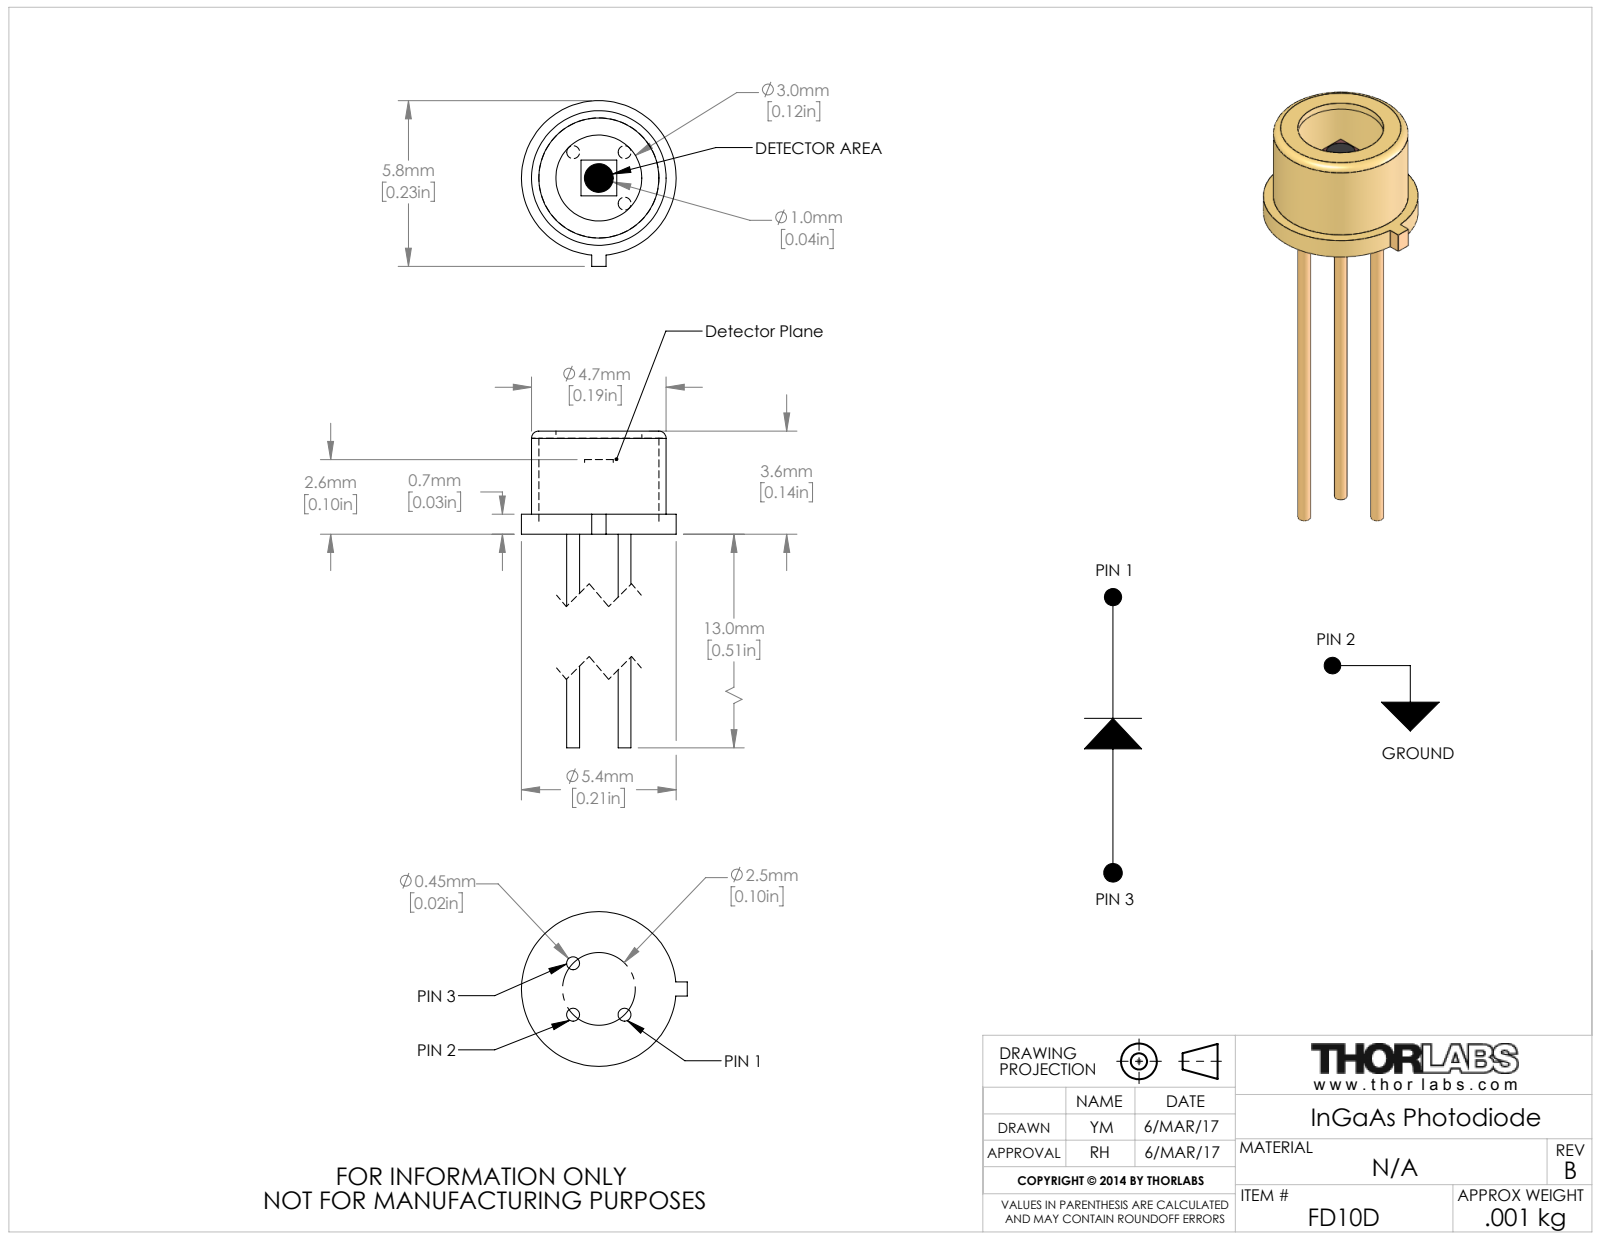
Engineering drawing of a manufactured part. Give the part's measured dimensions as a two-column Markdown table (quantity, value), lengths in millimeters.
| quantity | value |
| --- | --- |
| part name | TTN035386-E0W |
| STEP written by | SolidWorks 2014 (AUTOMOTIVE_DESIGN) |
| units | millimeters |
| bodies | 2 solids, 37 faces (18 planar, 17 cylindrical, 2 other) |
| overall size | 16.6 × 5.79 × 5.4 |
| volume | 31 mm³ |
| surface area | 213 mm² |
| round holes (diameter × count) | 3 × 1, 4.19 × 1 |
| round bosses / shafts (diameter × count) | 0.45 × 3, 5.4 × 1, 4.7 × 1, 1 × 1 |
| main face-to-face distances | 0.45, 2.9, 3.35, 3.6, 3.15, 0.7, 2.65, 2.45, 2, 1.75 |
